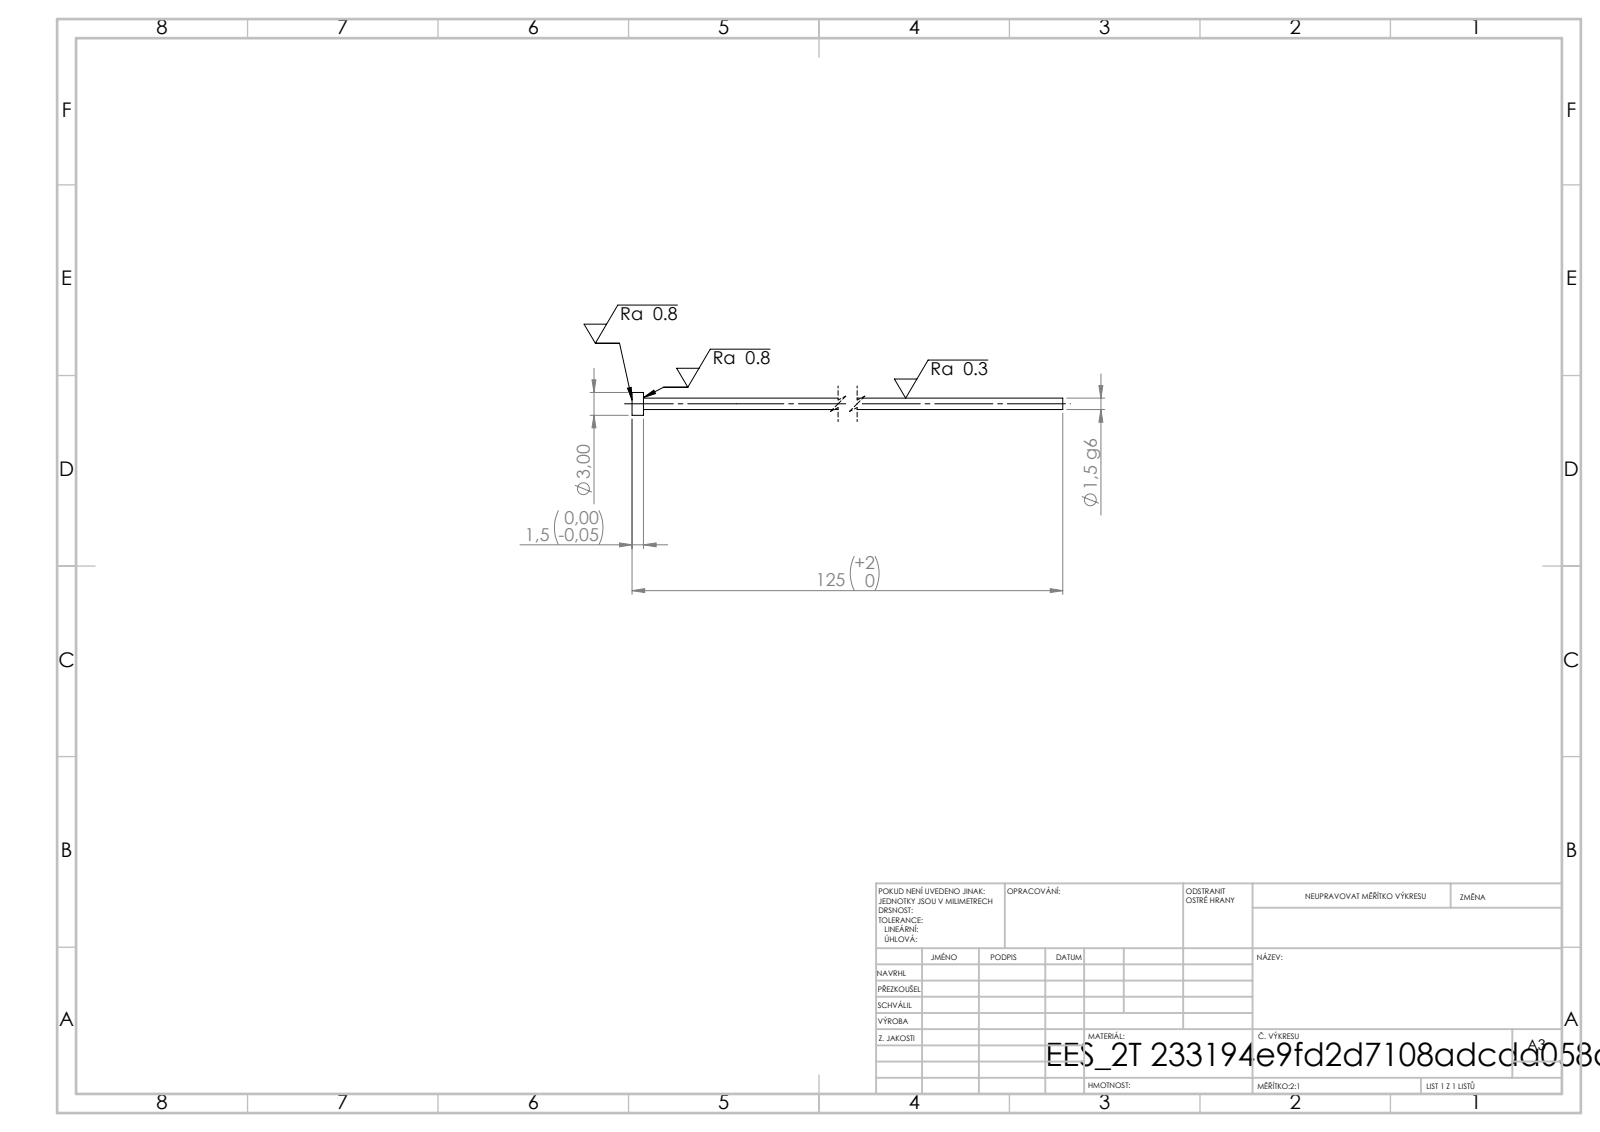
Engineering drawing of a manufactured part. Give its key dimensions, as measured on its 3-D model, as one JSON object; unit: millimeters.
{"step_written_by": "SolidWorks 2019 (CONFIG_CONTROL_DESIGN)", "units": "millimeters", "bodies": {"solids": 1, "faces": 7, "planar": 3, "cylindrical": 4, "other": 0}, "overall_size": [125, 3, 3], "volume_mm3": 229, "surface_area_mm2": 610, "round_bosses_or_shafts": [[3, 1], [1.5, 1]], "face_to_face_distances": [1.5, 125, 123.5]}
